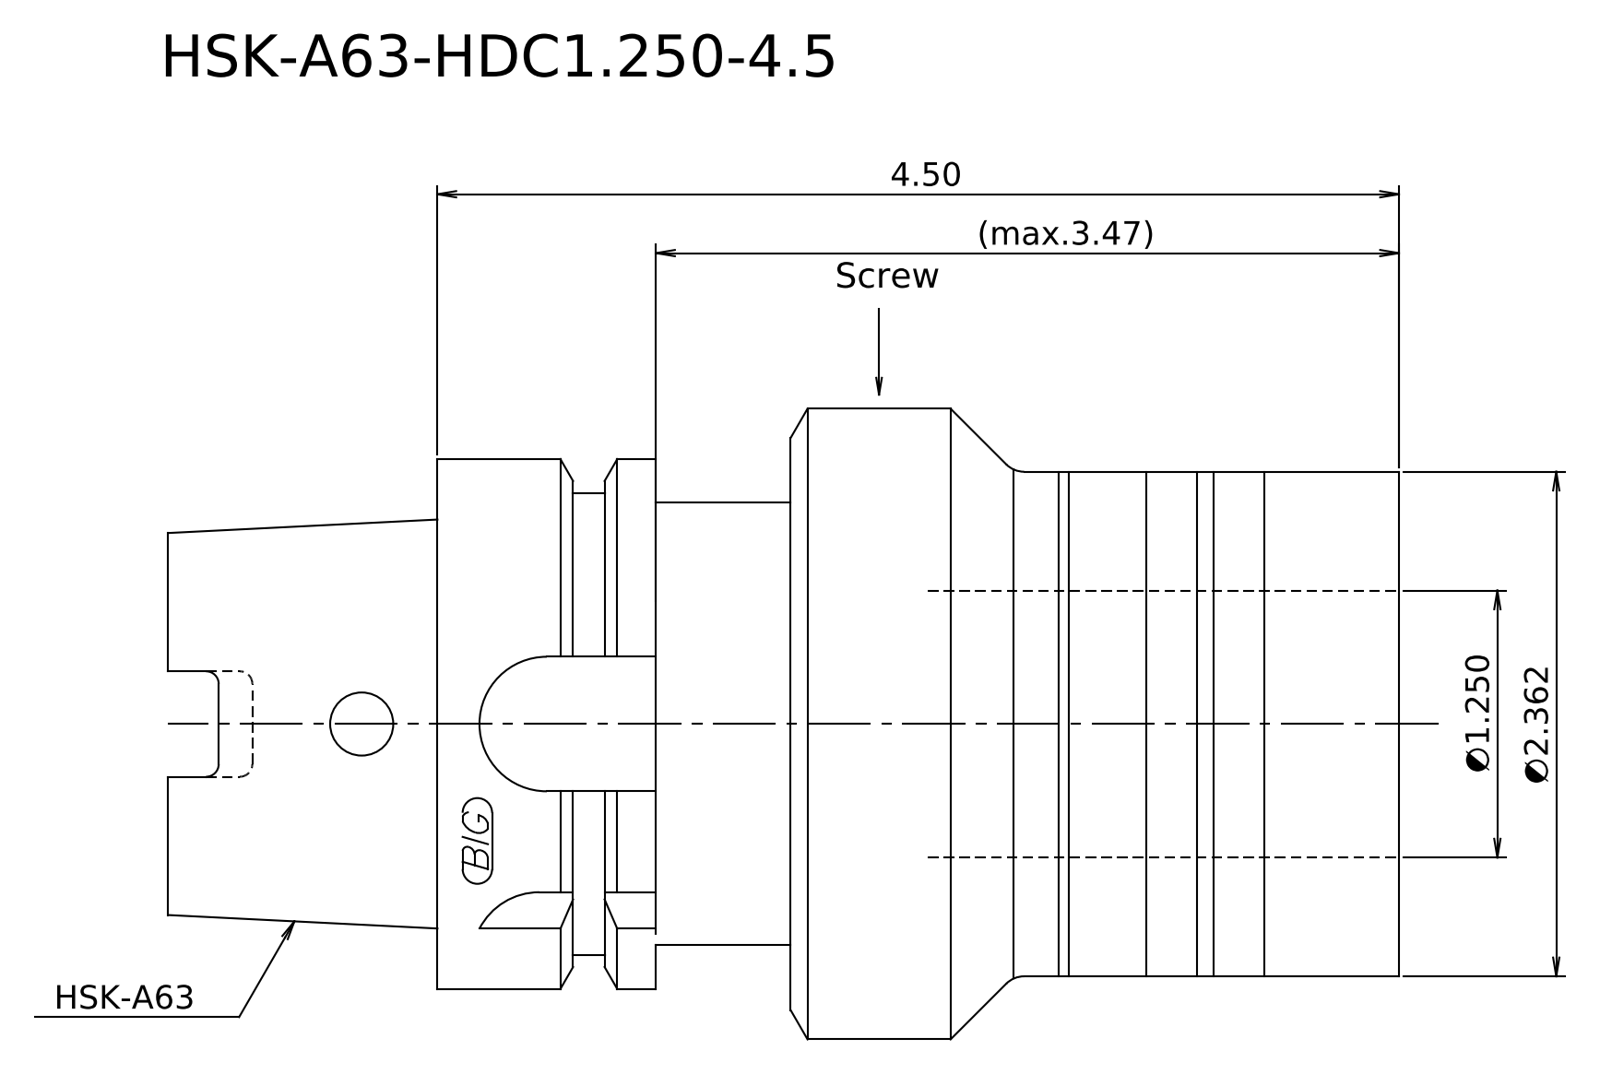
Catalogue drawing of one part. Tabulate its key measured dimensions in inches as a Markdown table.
| quantity | value |
| --- | --- |
| STEP written by | Kubotek KeyCreator 2011 V10.0.2 (22737) (automotive_design) |
| units | inches |
| bodies | 1 solid, 18 faces (7 planar, 6 cylindrical, 5 other) |
| overall size | 5.76 × 2.953 × 2.953 |
| volume | 24.92 in³ |
| surface area | 57.87 in² |
| round bosses / shafts (diameter × count) | 2.953 × 1, 2.48 × 1, 2.362 × 1, 2.165 × 1, 2.071 × 1 |
| main face-to-face distances | 5.76, 2.846, 2.913, 4.5, 1.654, 1.26, 3.476, 0.63, 1.024, 2.283 |
